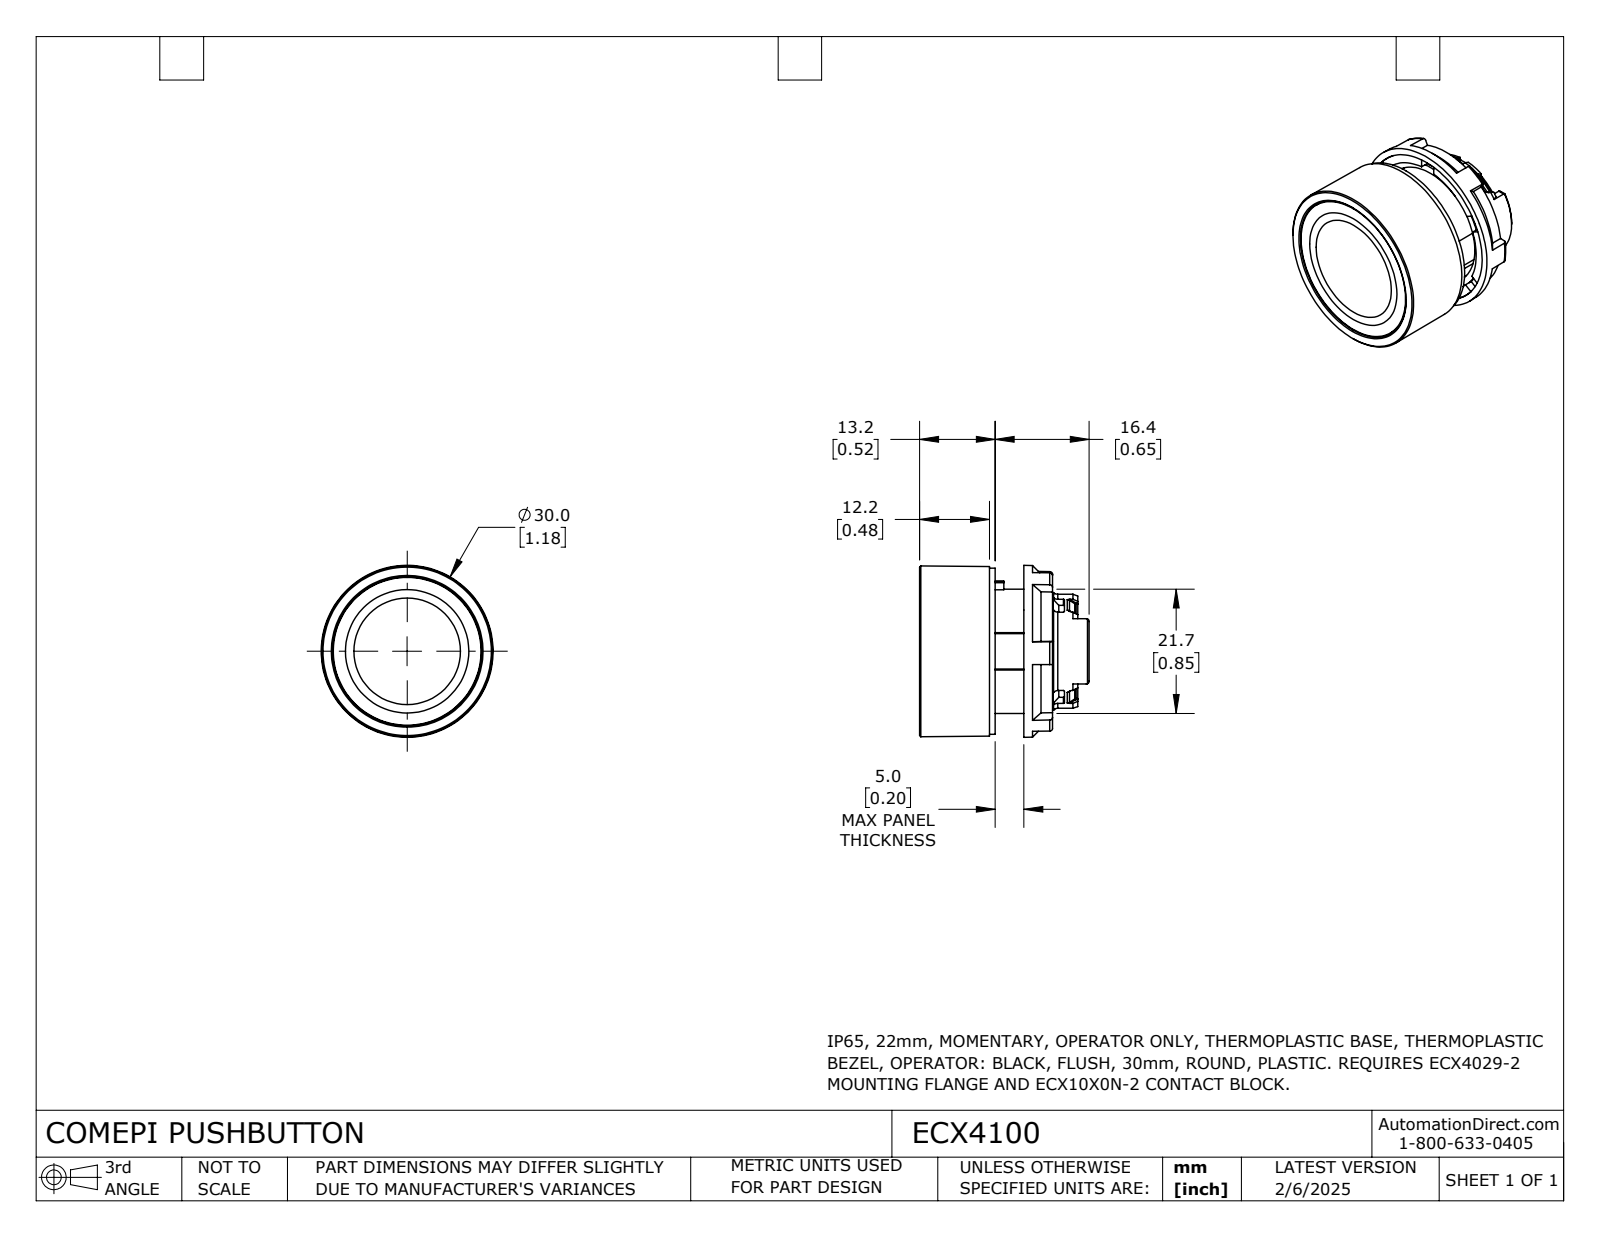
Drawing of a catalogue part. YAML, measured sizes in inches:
part_name: "ECX4100"
step_written_by: "SolidWorks 2024 (CONFIG_CONTROL_DESIGN)"
units: inches
bodies: {solids: 3, faces: 398, planar: 134, cylindrical: 111, other: 153}
overall_size: [1.181, 1.181, 1.165]
volume: 0.472
surface_area: 16.55
round_holes:
  - {diameter: 0.531, count: 1}
  - {diameter: 0.713, count: 1}
  - {diameter: 0.866, count: 1}
round_bosses_or_shafts:
  - {diameter: 1.142, count: 1}
  - {diameter: 1.016, count: 1}
  - {diameter: 0.965, count: 1}
  - {diameter: 0.854, count: 1}
  - {diameter: 0.807, count: 1}
  - {diameter: 0.787, count: 1}
  - {diameter: 0.748, count: 1}
  - {diameter: 0.728, count: 1}
partial_cylinders:
  - {radius: 0.008, count: 24}
  - {radius: 0.02, count: 8}
  - {radius: 0.01, count: 2}
  - {radius: 0.293, count: 1}
  - {radius: 0.344, count: 1}
  - {radius: 0.348, count: 1}
  - {radius: 0.366, count: 1}
face_to_face_distances: [0.409, 0.039, 0.433, 0.472, 0.236, 0.394, 0.197, 0.449, 0.512, 0.217]
